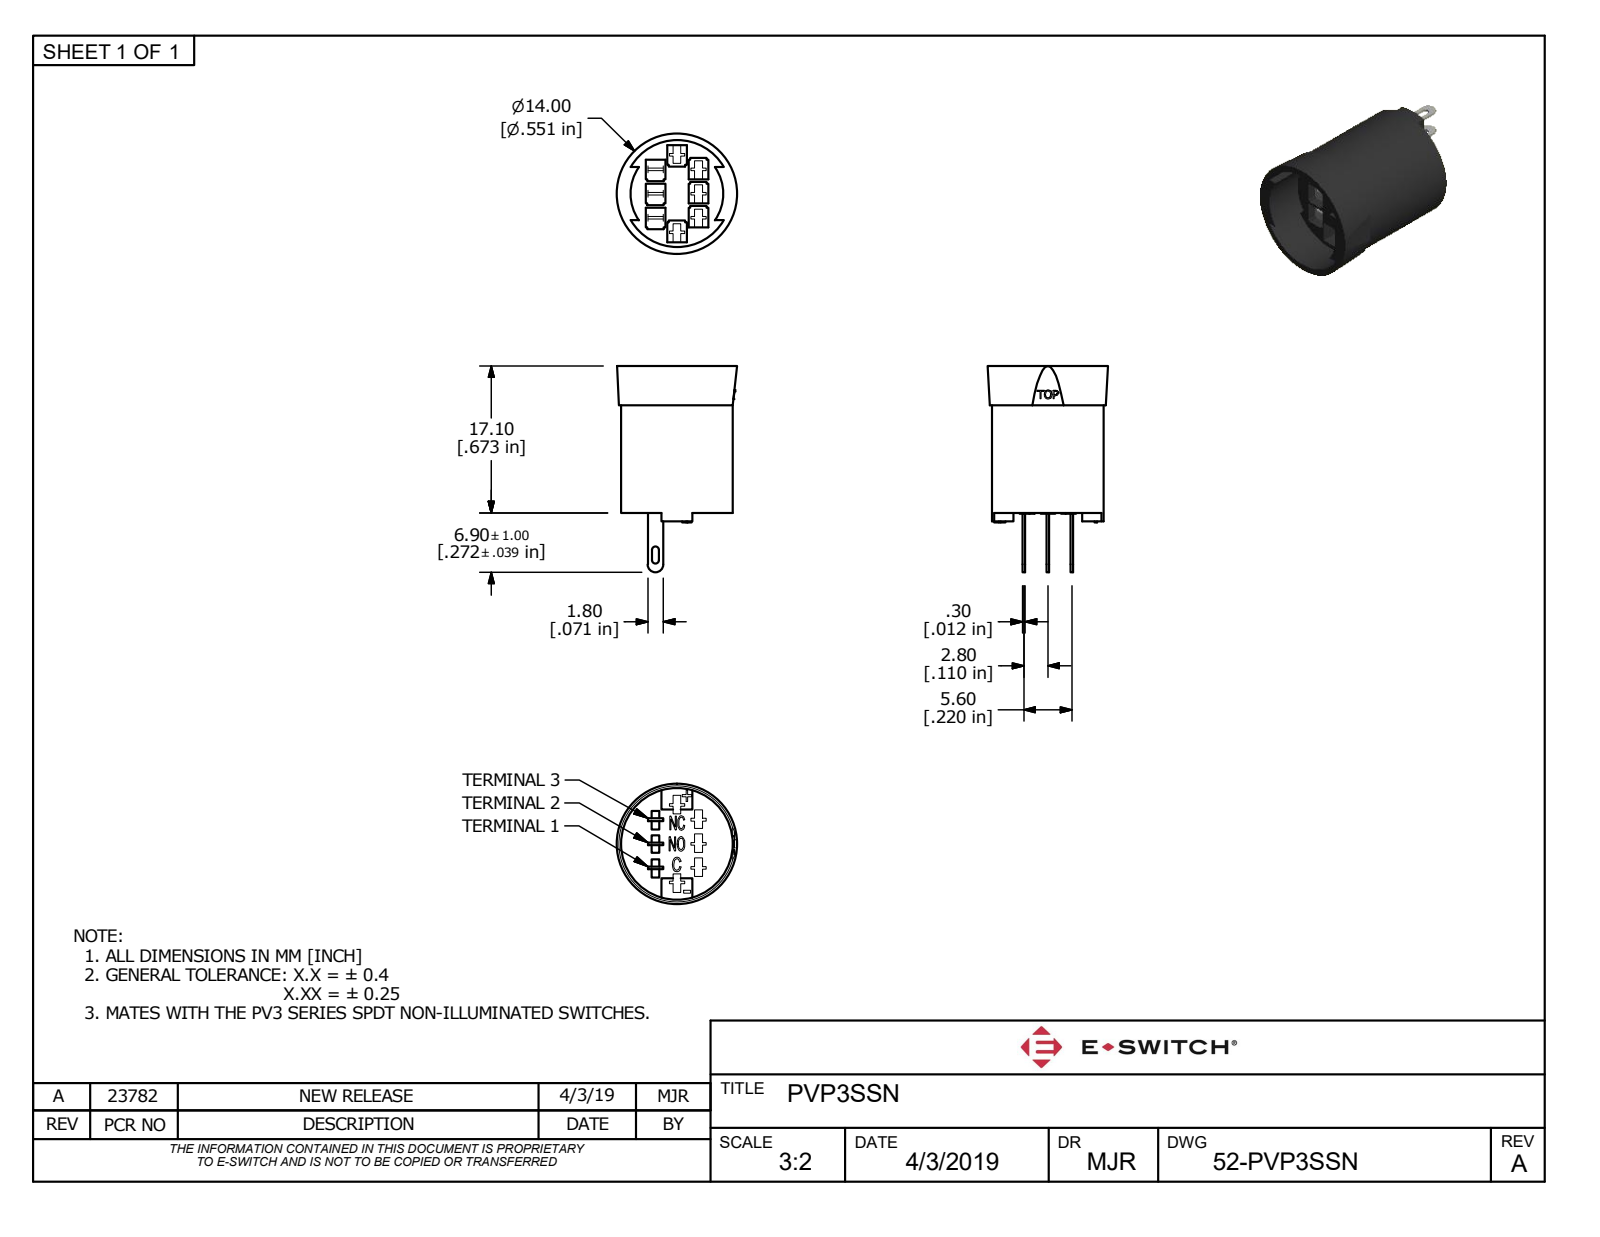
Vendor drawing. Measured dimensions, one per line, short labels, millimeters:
name: PVP3SSN
written by: Autodesk Inventor 2018 (AP242_MANAGED_MODEL_BASED_3D_ENGINEERING_MIM_LF)
unit: mm
bodies: 1 solid, 342 faces (272 planar, 20 cylindrical, 50 other)
size: 24 × 14 × 14
volume: 1 503 mm³; area: 2 051 mm²
bosses: 1× ⌀13
rounds: 6× R0.25, 2× R0.4, 2× R6.25, 1× R0.9, 1× R5.4
face distances: 2.5, 2.8, 1.5, 2.3, 1.8, 4.1, 1.6, 1.3, 4.3, 1
